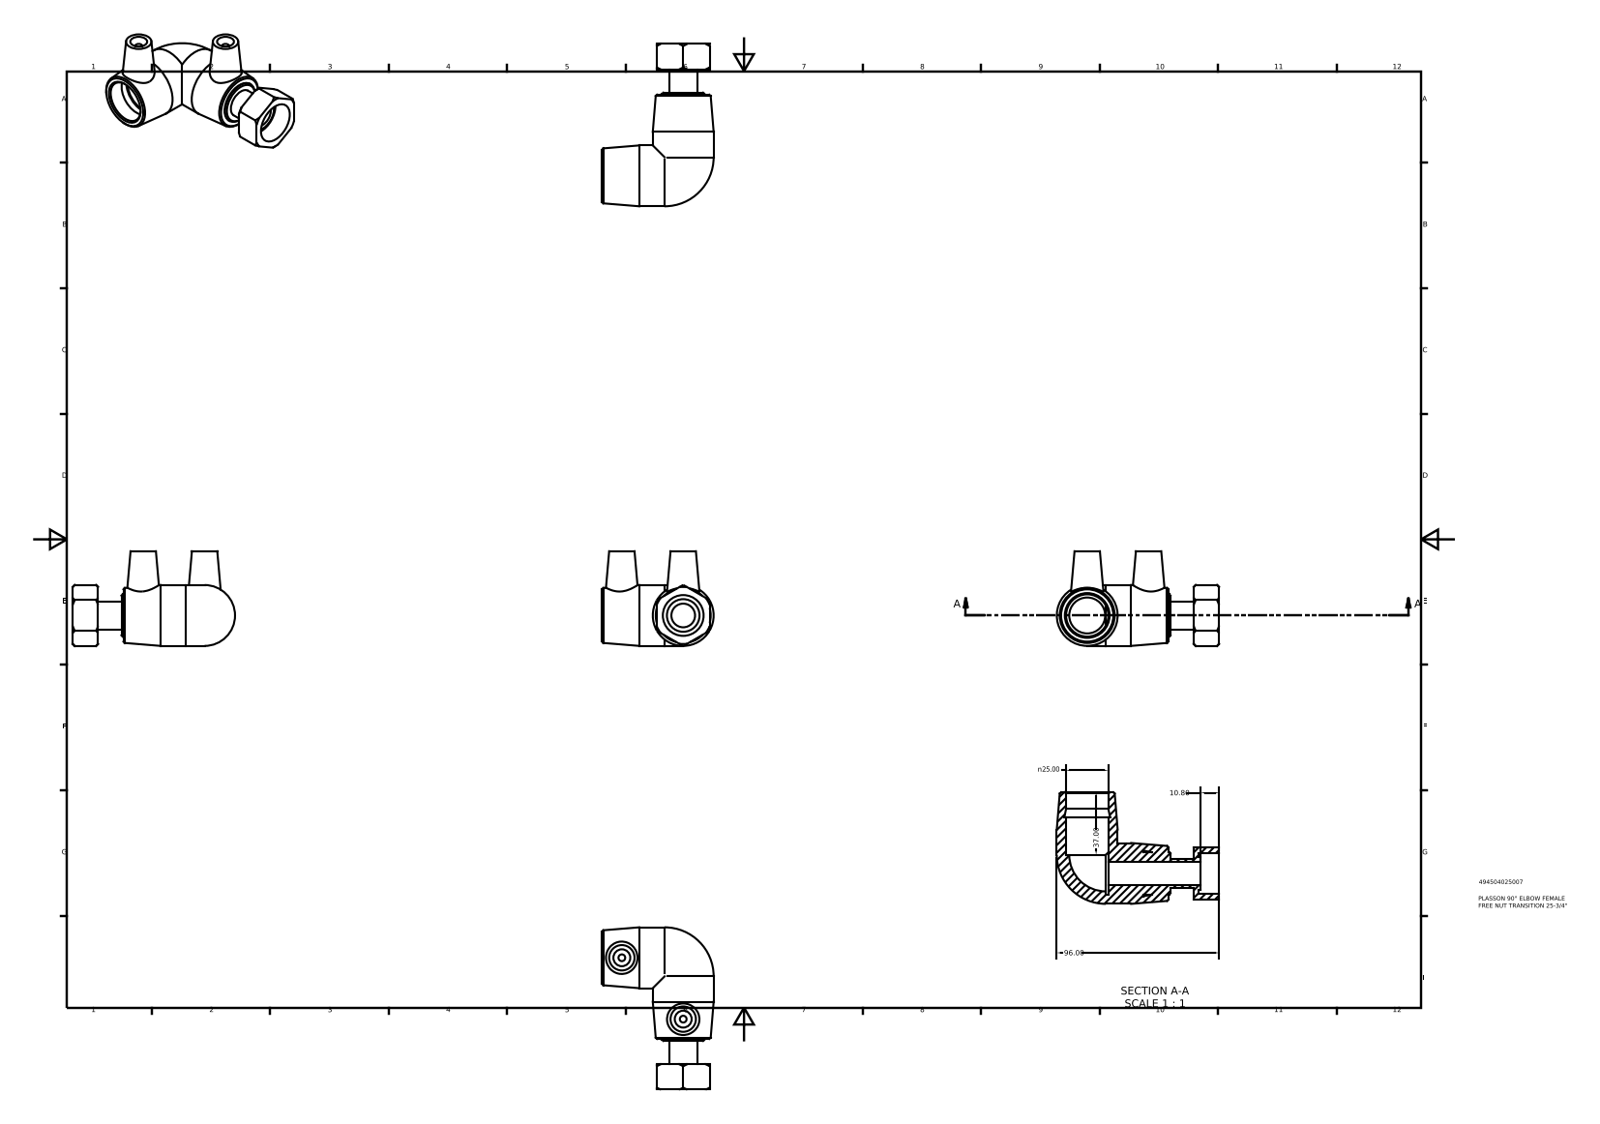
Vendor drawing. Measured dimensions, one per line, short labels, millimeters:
name: 494504025007
written by: Autodesk Inventor 2015 (AUTOMOTIVE_DESIGN)
unit: mm
bodies: 1 solid, 63 faces (24 planar, 15 cylindrical, 24 other)
size: 96 × 66 × 56.09
volume: 73 697 mm³; area: 26 989 mm²
holes: 2× ⌀10, 1× ⌀14, 1× ⌀24.12, 1× ⌀25
bosses: 2× ⌀36, 2× ⌀4, 1× ⌀25, 1× ⌀19.29, 1× ⌀16.88
face distances: 31.32, 15, 1.2, 50.5, 65.5, 18, 35.5, 30, 37, 36.7
hole spacings: 51.34
